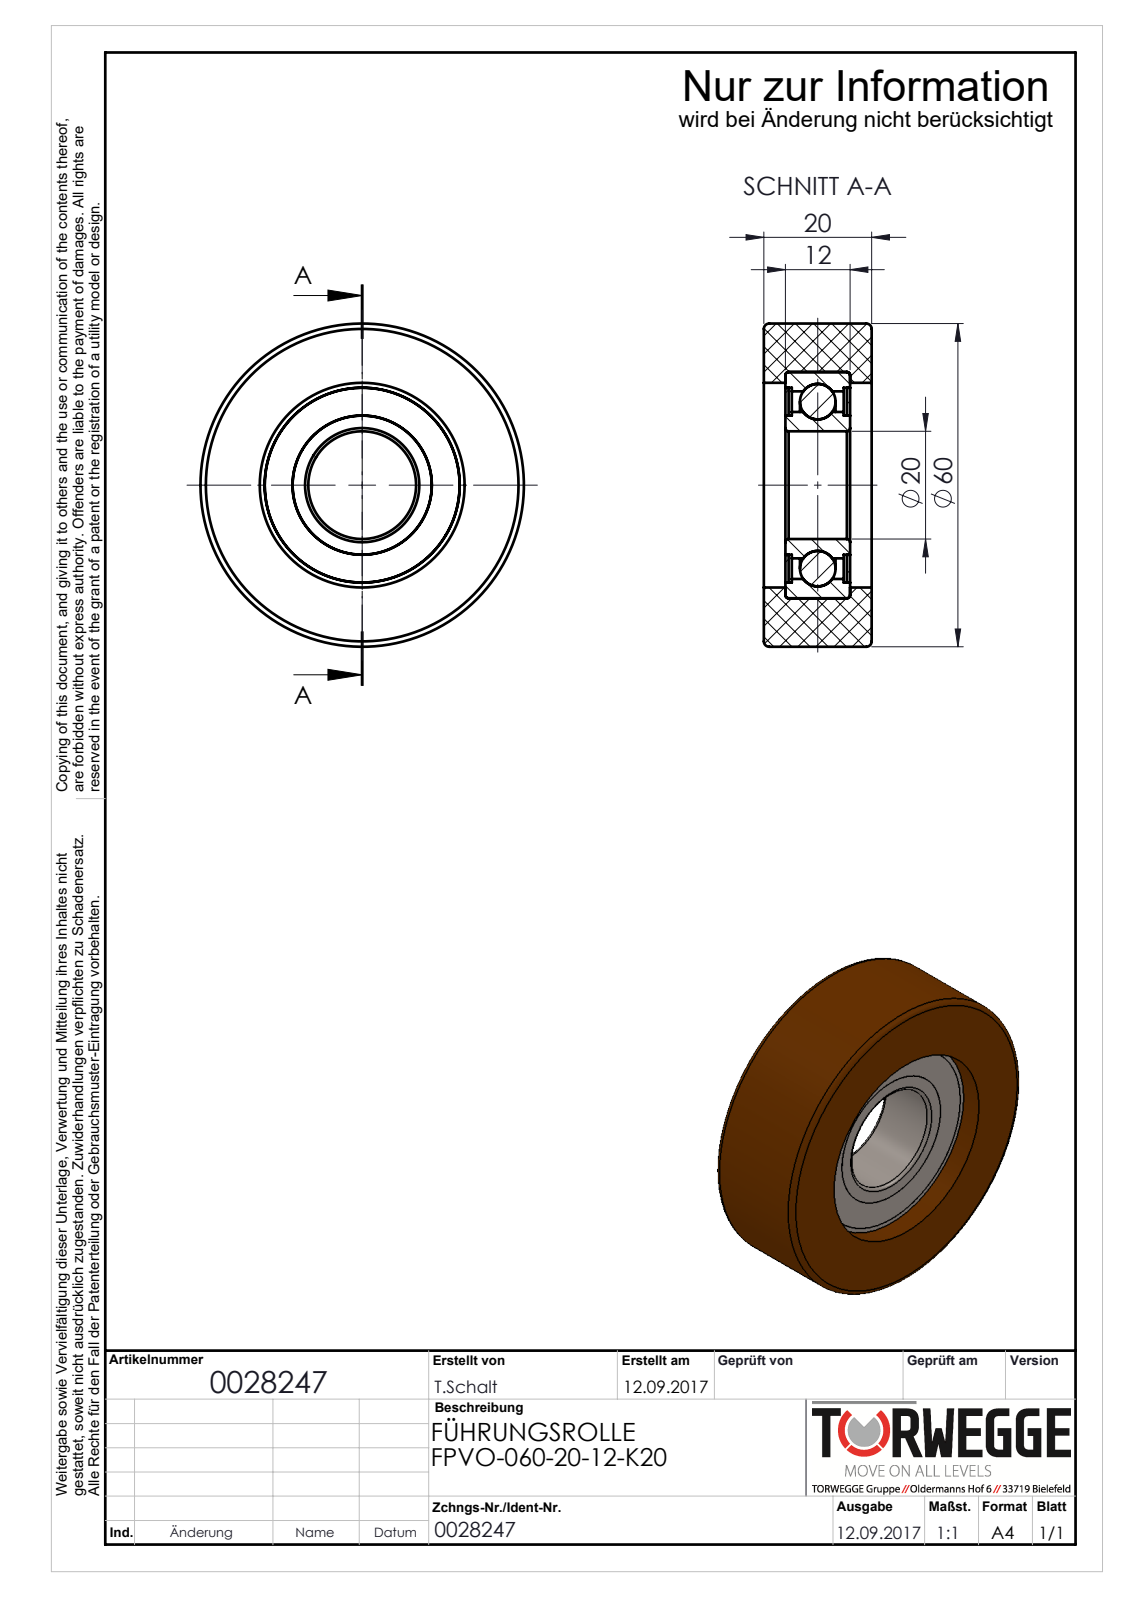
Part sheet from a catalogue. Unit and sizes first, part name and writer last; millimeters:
Units: millimetres
Overall size (bounding box): 60 × 60 × 20
Round holes (diameter × count): ⌀20 ×1, ⌀25.83 ×1, ⌀34.83 ×1, ⌀36.17 ×1, ⌀38 ×1, ⌀42 ×1
Round bosses / shafts (diameter × count): ⌀60 ×1, ⌀27.17 ×1
Main face-to-face distances: 4, 16, 20, 12, 10.81, 0.59, 0.6, 4.59, 11.41, 15.41
Volume: 41 744 mm³ · Surface area: 20 379 mm²
Bodies: 6 solids, 78 faces (16 planar, 36 cylindrical, 26 other)
Part name (STEP PRODUCT): FPVO-060-20-12-K20_Bandage; 0028247_FPVO-060-20-12-K20; 0029541_Rillenkugellager_DIN625-6004-20-ZZ
STEP written by: SolidWorks 2016 (AUTOMOTIVE_DESIGN)
